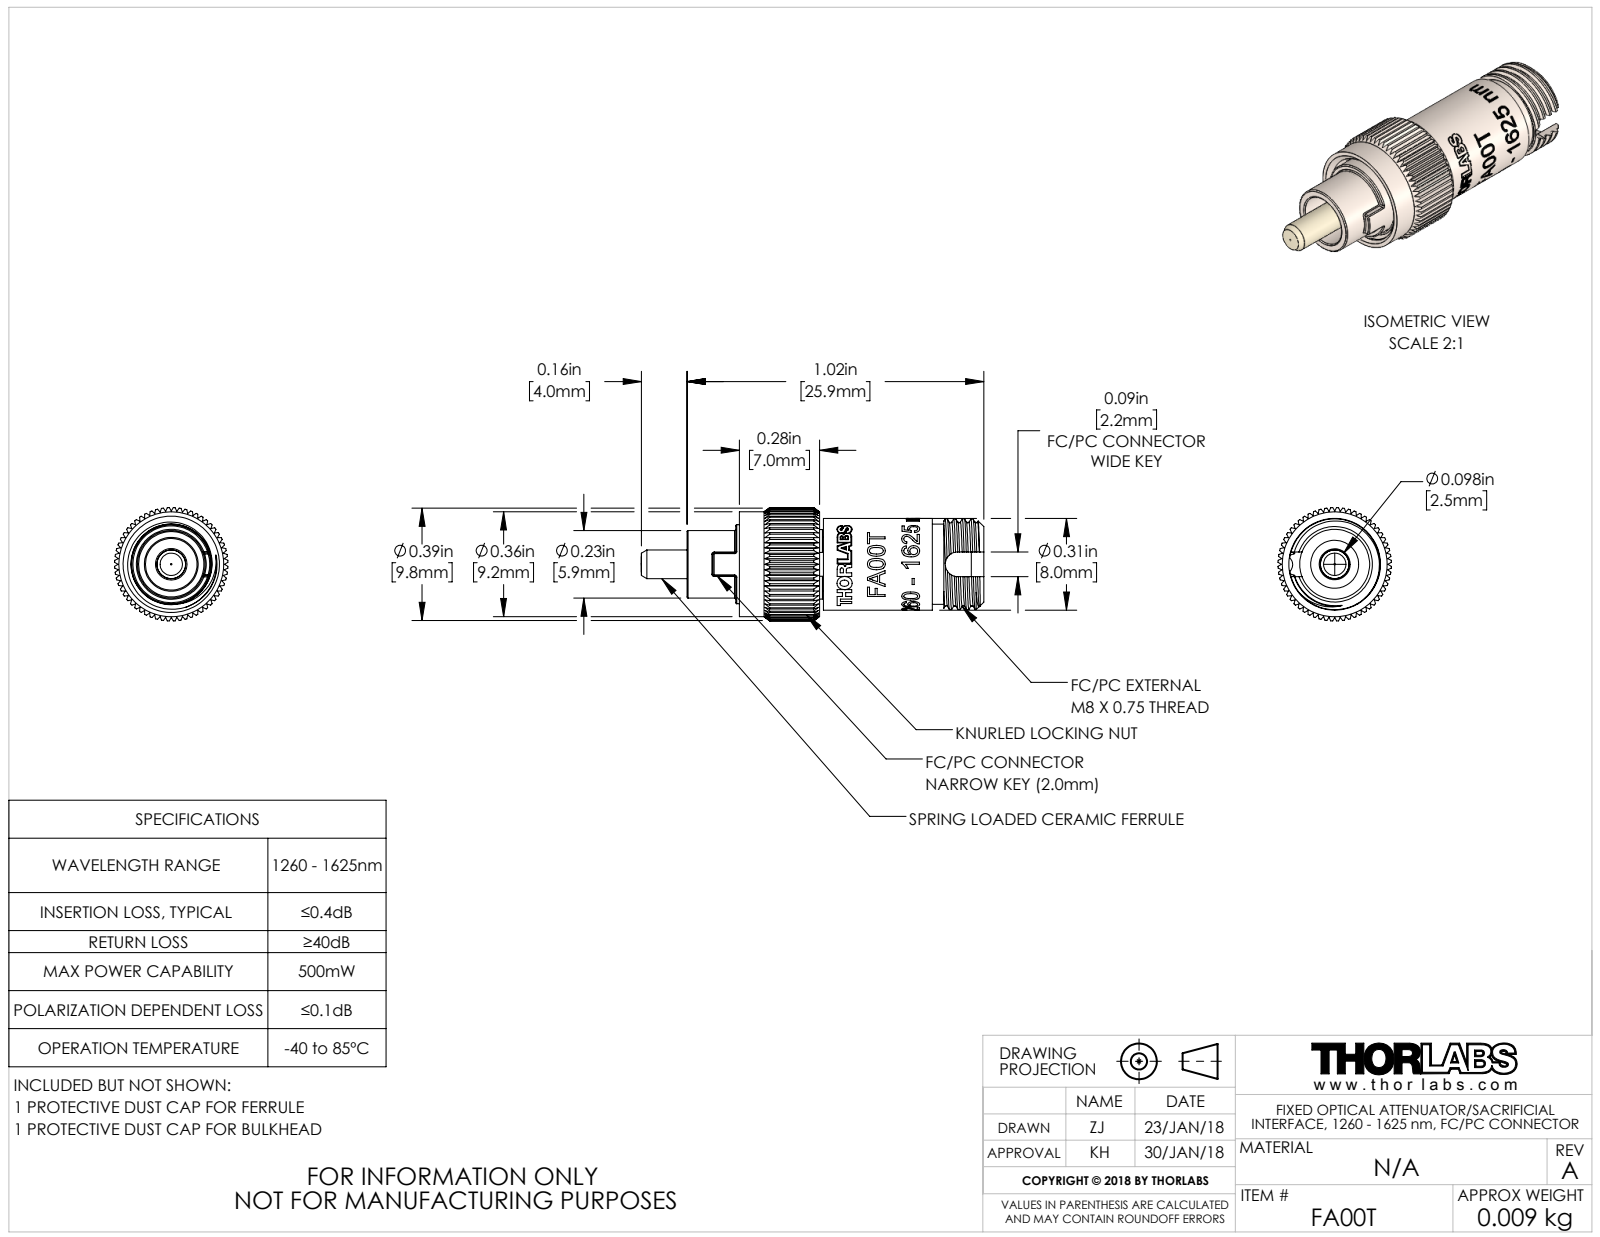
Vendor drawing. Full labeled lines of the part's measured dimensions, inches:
Part name (STEP PRODUCT): TTN148897-E0W
STEP written by: SolidWorks 2016 (CONFIG_CONTROL_DESIGN)
Units: inches
Bodies: 10 solids, 558 faces (190 planar, 252 cylindrical, 116 other)
Overall size (bounding box): 1.178 × 0.39 × 0.39
Volume: 0.058 in³ · Surface area: 4.625 in²
Round holes (diameter × count): ⌀0.039 ×1, ⌀0.071 ×1, ⌀0.098 ×1, ⌀0.106 ×1, ⌀0.108 ×1, ⌀0.138 ×1, ⌀0.169 ×1, ⌀0.198 ×1, ⌀0.225 ×1, ⌀0.24 ×1, ⌀0.246 ×1, ⌀0.246 ×1
Round bosses / shafts (diameter × count): ⌀0.36 ×1, ⌀0.315 ×1, ⌀0.312 ×1, ⌀0.276 ×1, ⌀0.272 ×1, ⌀0.241 ×1, ⌀0.239 ×1, ⌀0.236 ×1
Partial cylindrical surfaces — rounded edges, fillets, slot ends (radius × count): R0.004 ×8, R0.01 ×2, R0.042 ×1, R0.195 ×1
Main face-to-face distances: 0.183, 0.177, 0.035, 0.298, 0.014, 0.191, 0.157, 0.312, 0.489, 0.263
